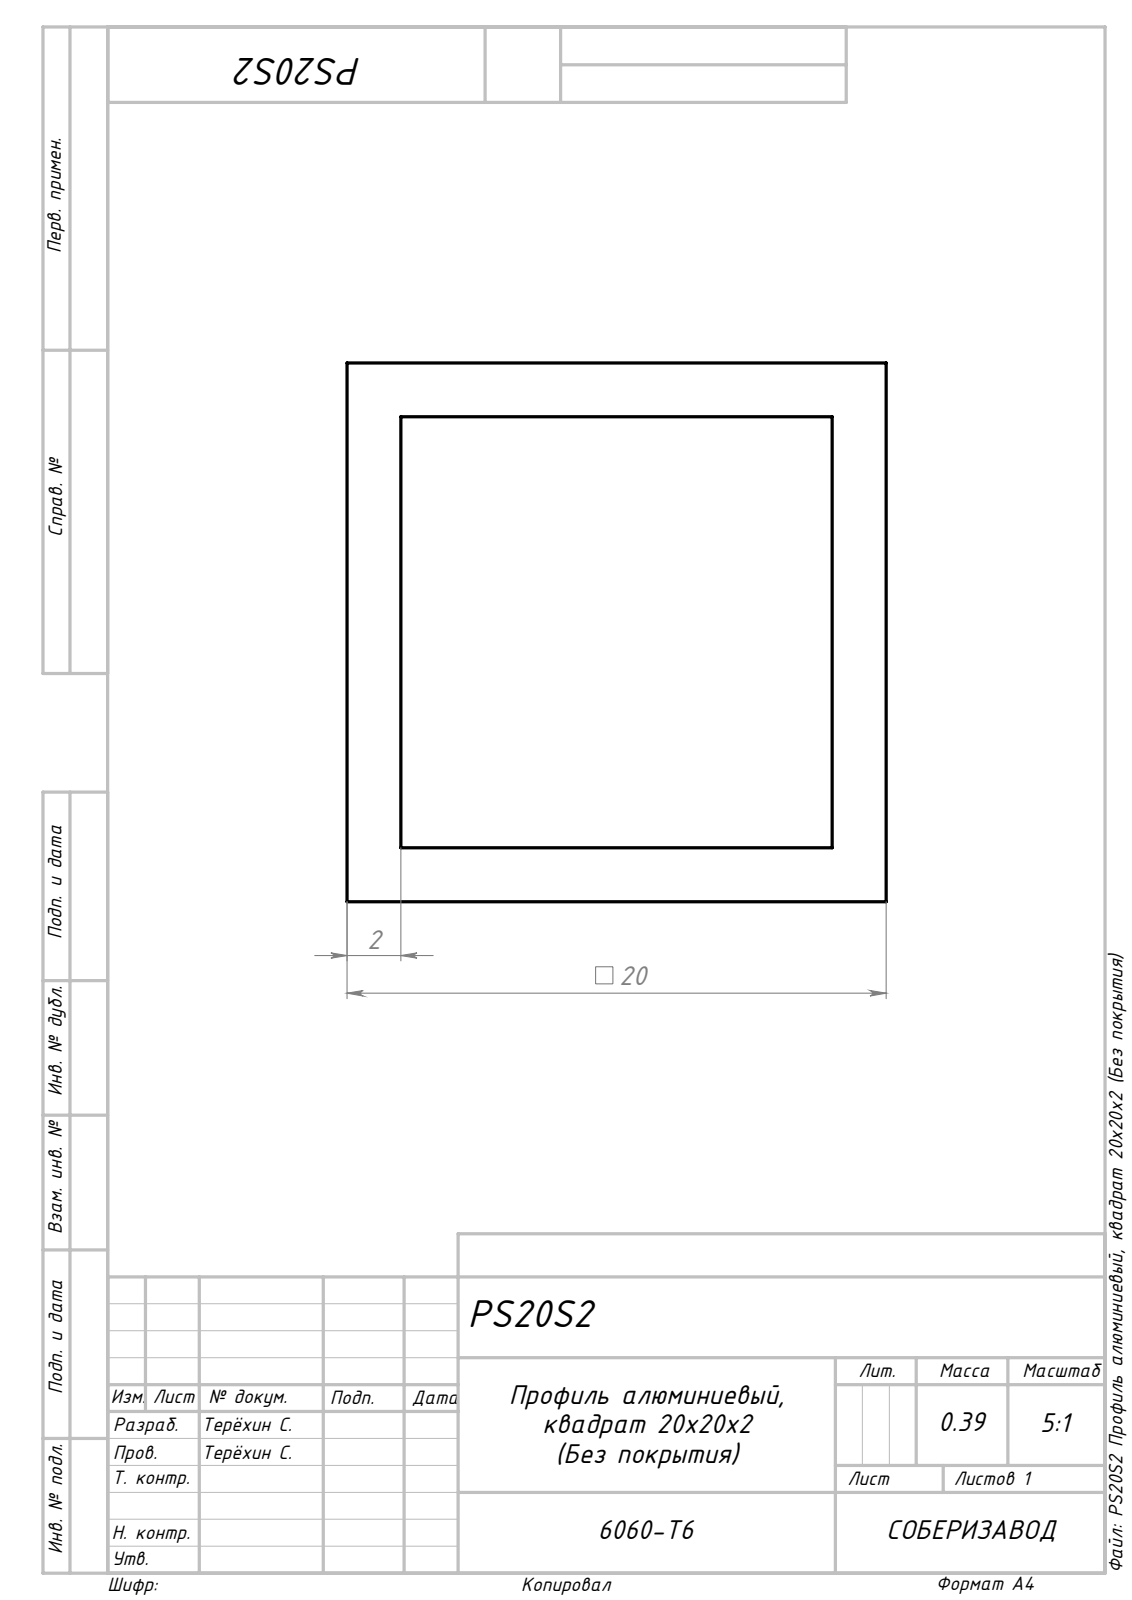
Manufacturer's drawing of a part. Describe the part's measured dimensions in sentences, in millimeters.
The part is named "PS20S2 Профиль алюминиевый, квадрат 20x20x2 (Без покрытия)_00; Сборка1". Its 3-D file was written by "SolidWorks 2024 (AUTOMOTIVE_DESIGN)". It is 1 solid with 10 faces: 10 planar, 0 cylindrical and 0 other. Overall it measures 1000 by 20 by 20 millimeters. Its volume is 144 000 cubic millimeters and its surface area 144 288 square millimeters. The main face-to-face distances are 18, 2, 20, 16, 1000.
